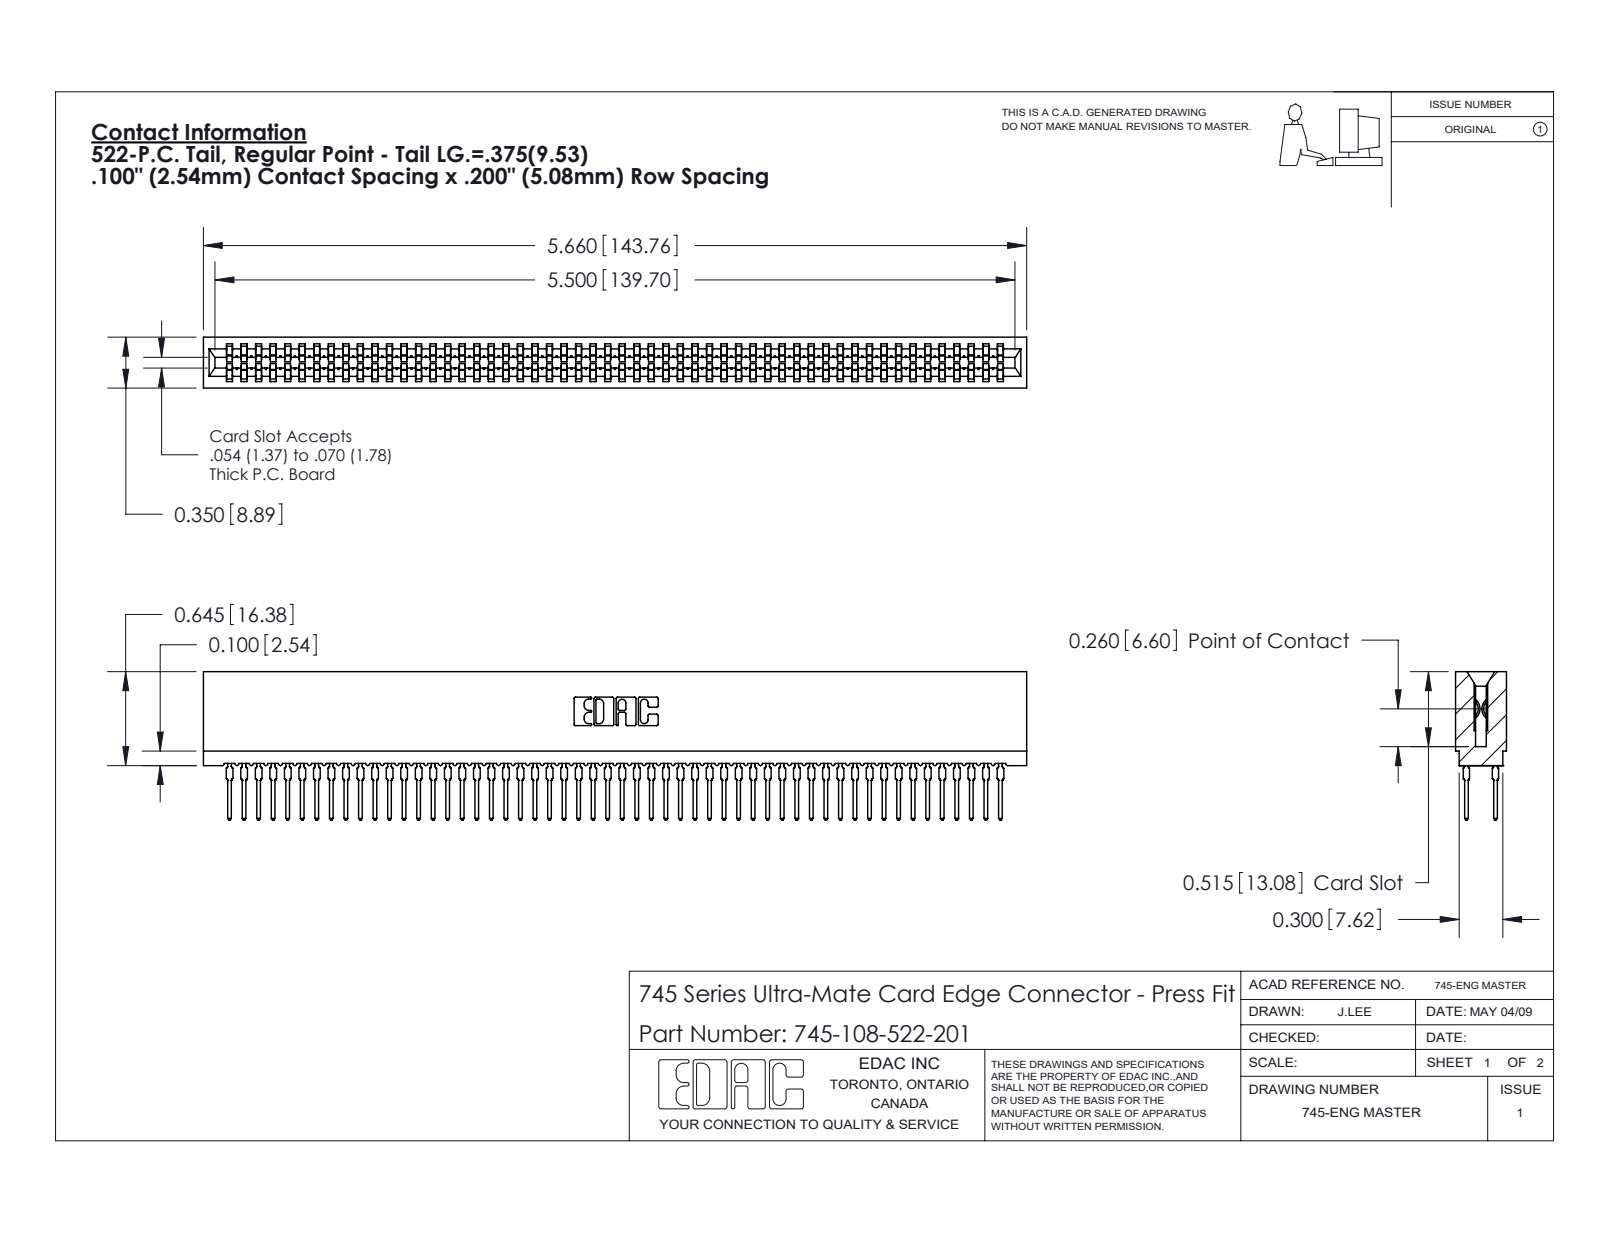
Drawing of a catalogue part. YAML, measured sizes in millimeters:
part_name: "745-292-001_522; 745 Part_Insulator Option - 01; 745-108-522-201"
step_written_by: "SolidWorks 2020 (CONFIG_CONTROL_DESIGN)"
units: millimeters
bodies: {solids: 109, faces: 9761, planar: 5023, cylindrical: 1930, other: 2808}
overall_size: [143.8, 25.9, 8.9]
volume: 13000
surface_area: 27060
partial_cylinders:
  - {radius: 0.5, count: 216}
  - {radius: 0.4, count: 108}
  - {radius: 0.3, count: 22}
  - {radius: 0.1, count: 8}
  - {radius: 0.3, count: 8}
  - {radius: 0.2, count: 6}
  - {radius: 0.8, count: 6}
  - {radius: 0.7, count: 3}
face_to_face_distances: [8.9, 1.6, 7.3, 5.1, 1.1, 7.7, 0.5, 6.2, 3.5, 5.4]
